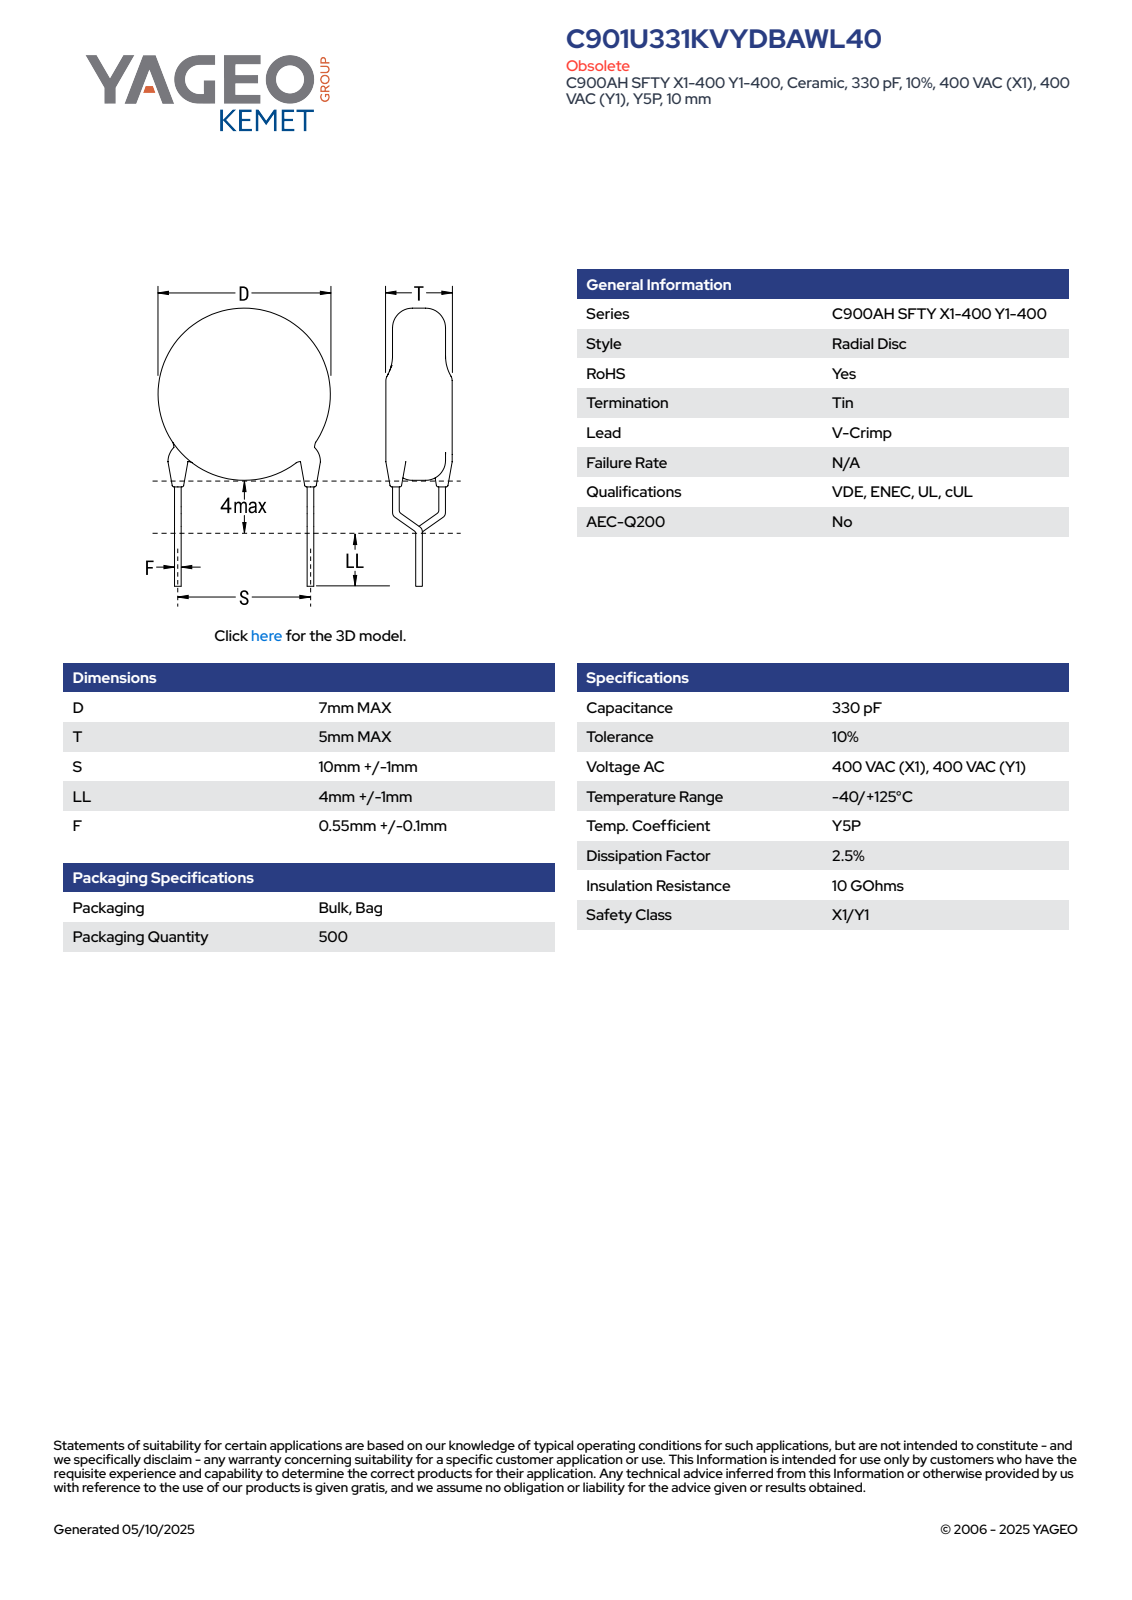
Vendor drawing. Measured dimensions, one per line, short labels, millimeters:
name: CCD_VCC900_D7T5S10LL5F0.65
written by: SolidWorks 2014 (AUTOMOTIVE_DESIGN)
unit: mm
bodies: 5 solids, 93 faces (65 planar, 16 cylindrical, 12 other)
size: 15.8 × 10.65 × 5
volume: 195 mm³; area: 227 mm²
bosses: 6× ⌀0.65, 1× ⌀7
face distances: 5, 7.9, 0.91, 12.75, 4.85, 11.84, 3.94, 3.71, 0.34, 1.87
